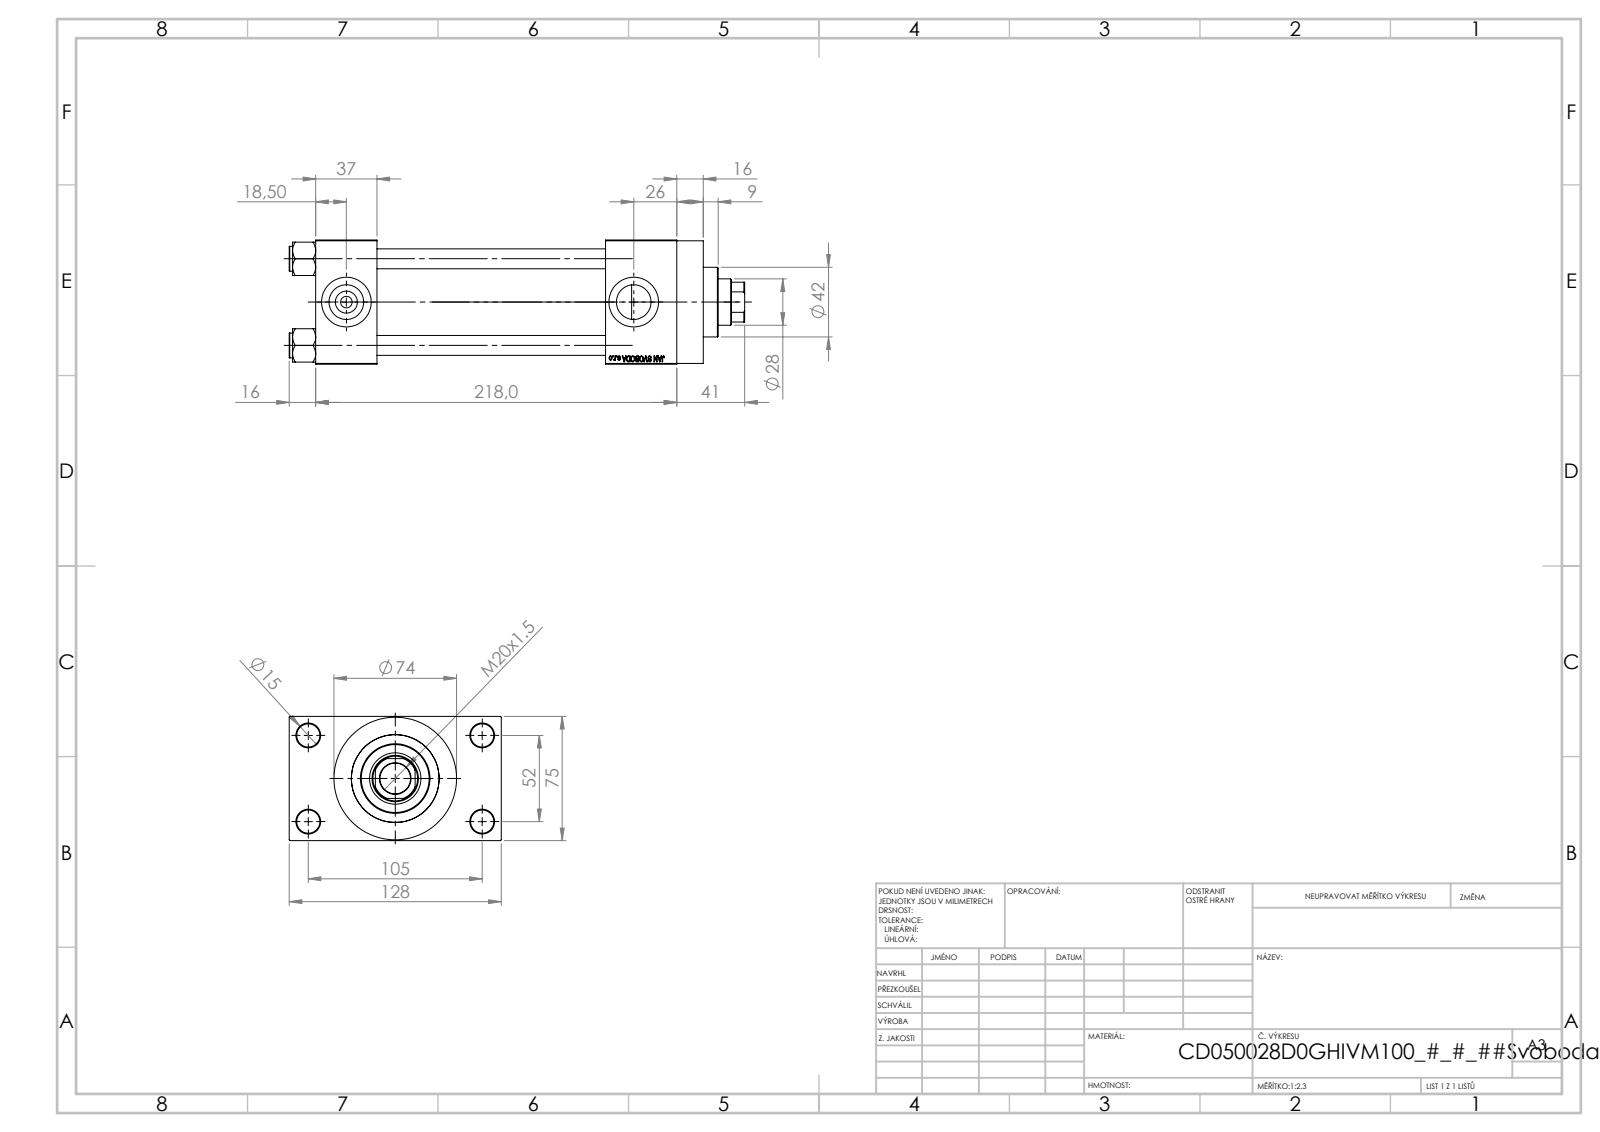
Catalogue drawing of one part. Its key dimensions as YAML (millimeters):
part_name: "V215CD_VC_A; V215CD_VCP_D; V215CD_NUT_M5_D; V215CD_D_Body (+1 more)"
step_written_by: "SolidWorks 2019 (CONFIG_CONTROL_DESIGN)"
units: millimeters
bodies: {solids: 11, faces: 1103, planar: 497, cylindrical: 88, other: 518}
overall_size: [275, 128, 75]
volume: 931622
surface_area: 216350
round_holes:
  - {diameter: 12, count: 4}
  - {diameter: 14, count: 4}
  - {diameter: 7, count: 2}
  - {diameter: 20.96, count: 2}
  - {diameter: 30, count: 2}
  - {diameter: 18.5, count: 1}
  - {diameter: 28, count: 1}
  - {diameter: 31, count: 1}
  - {diameter: 41, count: 1}
  - {diameter: 50, count: 1}
  - {diameter: 53, count: 1}
round_bosses_or_shafts:
  - {diameter: 15, count: 4}
  - {diameter: 74, count: 1}
  - {diameter: 56, count: 1}
  - {diameter: 42, count: 1}
partial_cylinders:
  - {radius: 13.5, count: 1}
face_to_face_distances: [75, 138, 37, 175, 26.5, 218, 181, 43, 101.5, 16]
hole_center_spacings: [26.35, 36.98, 52.3, 58.43, 58.59, 78.65, 94.37, 52]
